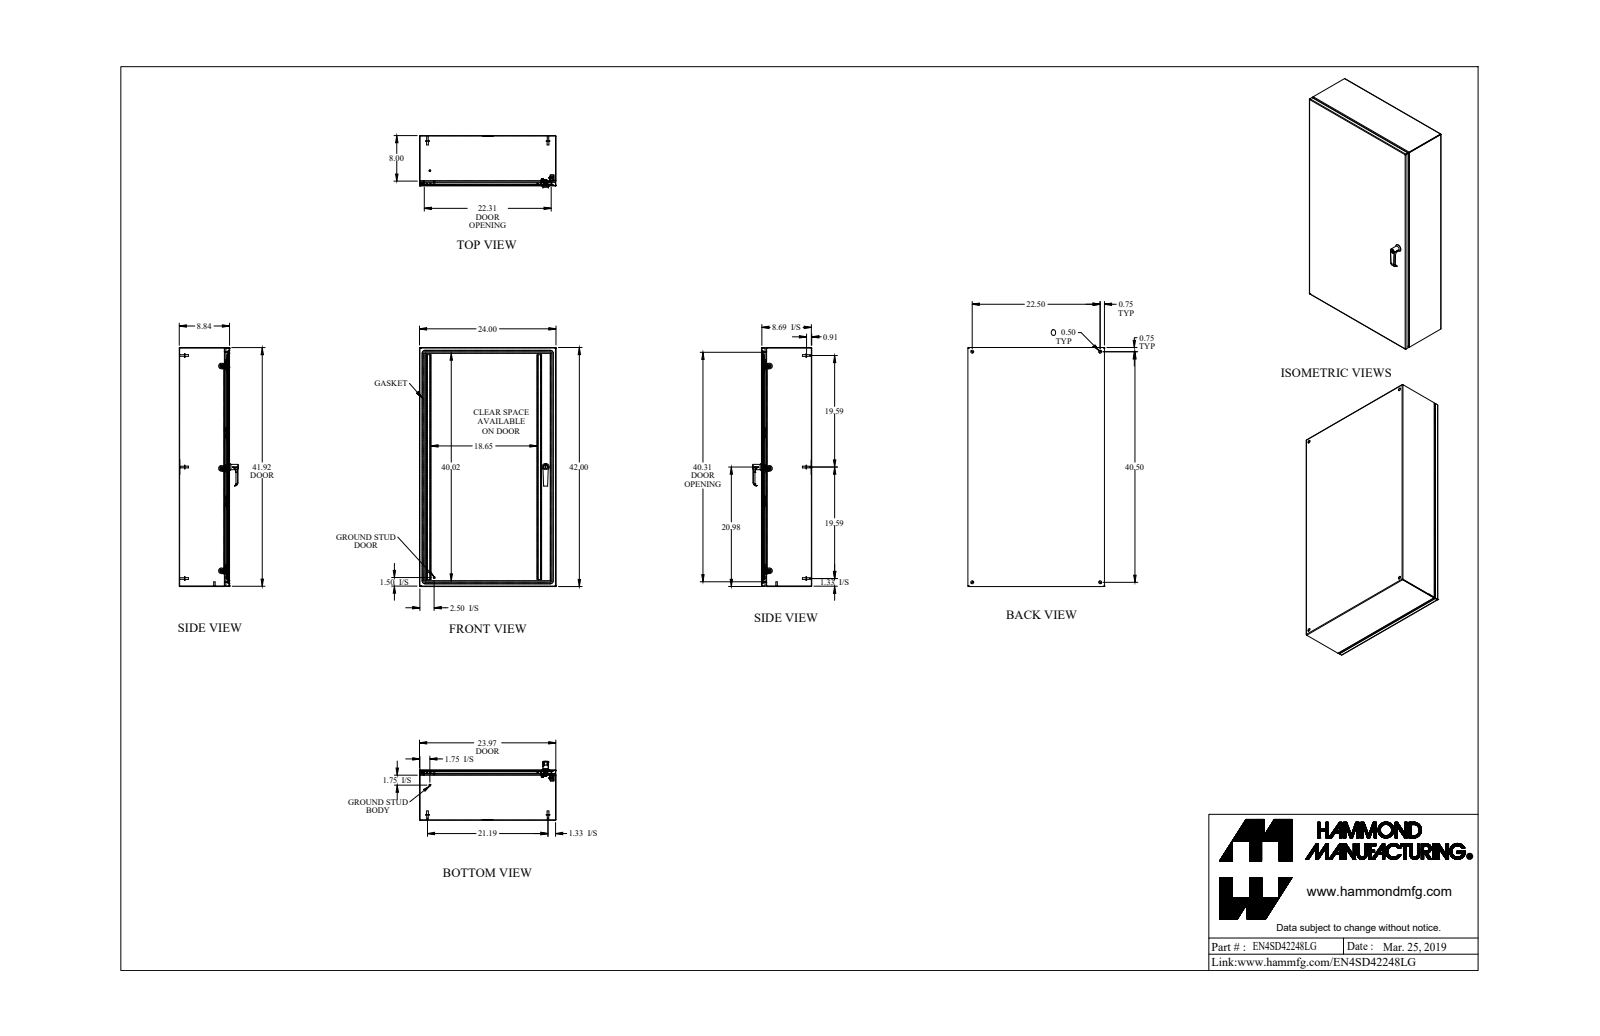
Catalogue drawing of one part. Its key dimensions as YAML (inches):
part_name: "EN4SD42248LG_Default"
step_written_by: "SolidWorks 2019 (CONFIG_CONTROL_DESIGN)"
units: inches
bodies: {solids: 53, faces: 1457, planar: 632, cylindrical: 538, other: 287}
overall_size: [42, 24, 10.367]
volume: 266.8
surface_area: 7397
round_holes:
  - {diameter: 0.176, count: 6}
  - {diameter: 0.5, count: 4}
  - {diameter: 0.196, count: 3}
  - {diameter: 0.25, count: 3}
  - {diameter: 0.265, count: 3}
  - {diameter: 0.413, count: 3}
  - {diameter: 0.172, count: 2}
  - {diameter: 0.242, count: 2}
  - {diameter: 0.256, count: 2}
  - {diameter: 0.313, count: 2}
  - {diameter: 0.394, count: 2}
  - {diameter: 0.24, count: 1}
round_bosses_or_shafts:
  - {diameter: 0.25, count: 7}
  - {diameter: 0.625, count: 6}
  - {diameter: 0.375, count: 6}
  - {diameter: 0.313, count: 6}
  - {diameter: 0.27, count: 6}
  - {diameter: 0.156, count: 6}
  - {diameter: 1, count: 3}
  - {diameter: 0.63, count: 2}
partial_cylinders:
  - {radius: 0.036, count: 20}
  - {radius: 0.108, count: 20}
  - {radius: 0.03, count: 15}
  - {radius: 0.043, count: 12}
  - {radius: 0.081, count: 12}
  - {radius: 0.006, count: 8}
  - {radius: 0.04, count: 8}
  - {radius: 0.062, count: 8}
face_to_face_distances: [0.072, 8.765, 8.693, 8.837, 23.928, 41.928, 23.856, 24, 41.856, 42]
hole_center_spacings: [0.787, 17.982, 18, 22.5, 35.969, 40.5, 46.33, 0.013]
